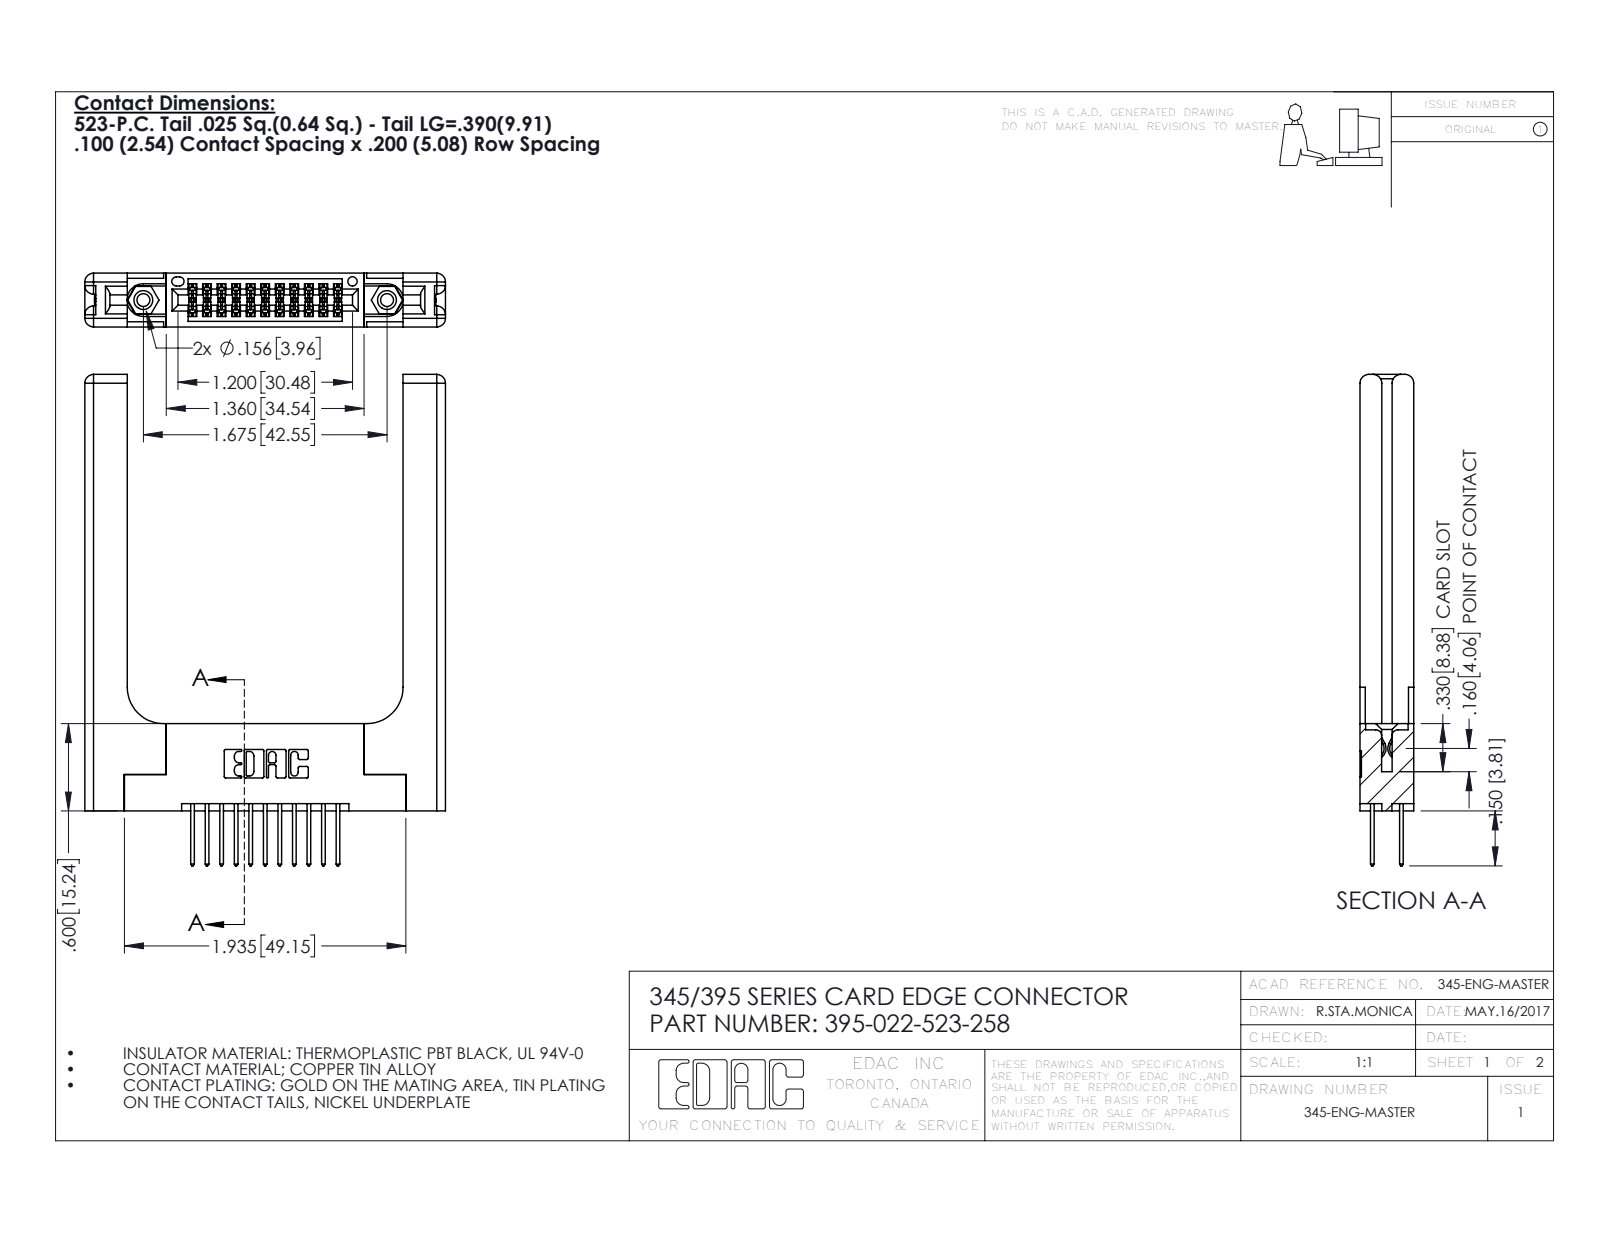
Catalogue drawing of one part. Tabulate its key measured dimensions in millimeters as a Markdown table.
| quantity | value |
| --- | --- |
| part name | 345-220-058_345-220-058; 345-250-001_345-250-001-102; 395-022-523-258; 345-292-001_345-293-123 (+1 more) |
| STEP written by | SolidWorks 2016 (CONFIG_CONTROL_DESIGN) |
| units | millimeters |
| bodies | 27 solids, 1482 faces (954 planar, 468 cylindrical, 60 other) |
| overall size | 85.8 × 63 × 9.4 |
| volume | 14 400 mm³ |
| surface area | 13 340 mm² |
| round holes (diameter × count) | 2.3 × 2, 3.2 × 2, 4 × 2, 1.6 × 1 |
| round bosses / shafts (diameter × count) | 3.9 × 2 |
| partial cylindrical surfaces (radius × count) | 0.2 × 33, 0.3 × 22, 0.3 × 22, 1.5 × 16, 0.2 × 6, 0.8 × 6, 0.7 × 3, 0.4 × 2 |
| main face-to-face distances | 9.4, 1.8, 7.6, 2, 3.8, 3.8, 5.1, 5.6, 5.7, 2.5 |
| hole center spacings | 6.9, 36.7, 42.5 |
